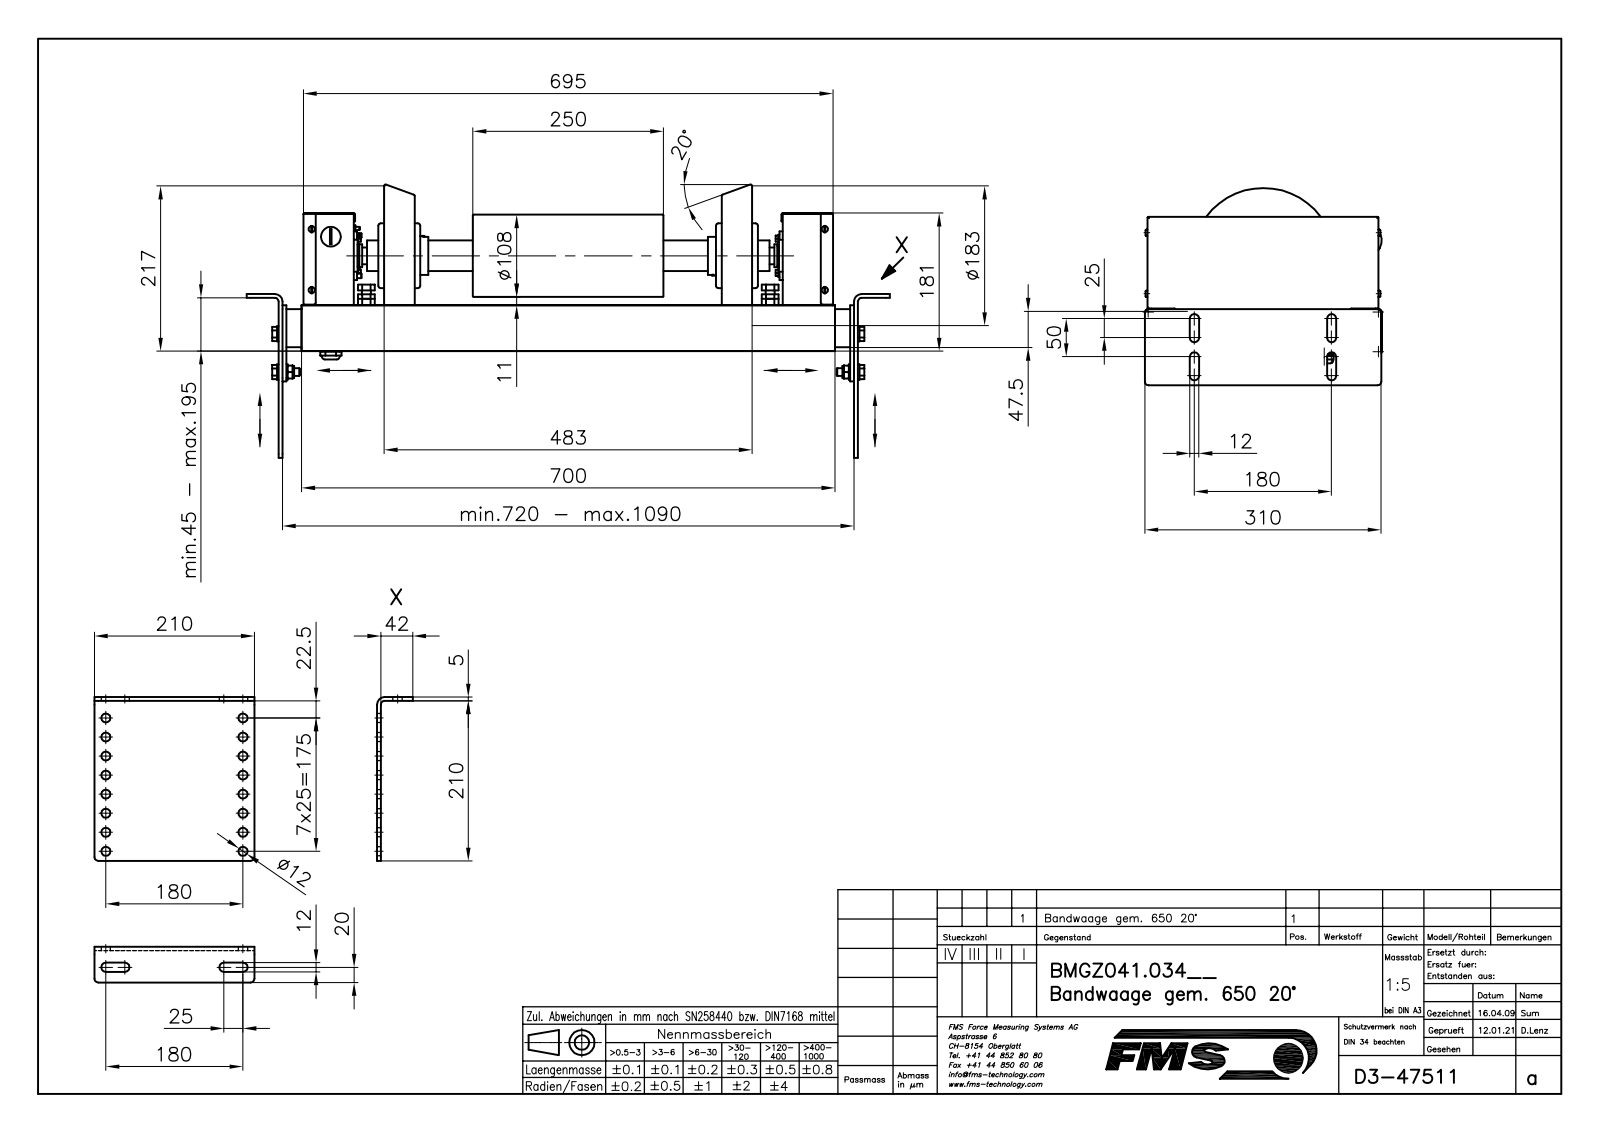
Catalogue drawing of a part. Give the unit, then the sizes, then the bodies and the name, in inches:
Units: inches
Overall size (bounding box): 33.228 × 14.122 × 12.232
Round holes (diameter × count): ⌀0.472 ×17, ⌀0.197 ×6, ⌀0.138 ×4, ⌀0.193 ×4, ⌀0.252 ×4, ⌀0.342 ×4, ⌀0.344 ×4, ⌀0.394 ×4, ⌀0.413 ×4, ⌀0.42 ×4, ⌀0.583 ×4, ⌀0.161 ×3
Round bosses / shafts (diameter × count): ⌀0.472 ×11, ⌀0.323 ×8, ⌀0.165 ×8, ⌀0.787 ×6, ⌀0.394 ×6, ⌀0.197 ×5, ⌀0.63 ×4, ⌀0.437 ×4
Partial cylindrical surfaces — rounded edges, fillets, slot ends (radius × count): R0.079 ×34, R0.039 ×24, R0.157 ×16, R0.197 ×16, R0.236 ×14, R0.138 ×8, R0.089 ×6, R0.02 ×4
Main face-to-face distances: 0.157, 0.197, 0.039, 10.63, 1.417, 10.472, 1.26, 2.205, 10.787, 1.575
Hole centre spacings: 0.984, 7.155, 1.969, 7.355, 2.953, 7.677, 3.937, 7.087
Volume: 380.3 in³ · Surface area: 4 915 in²
Bodies: 161 solids, 2732 faces (1379 planar, 974 cylindrical, 379 other)
Part name (STEP PRODUCT): B47511_STP; B50029; B46957; B4695602 (+8 more)
STEP written by: Mechanical Desktop 2009 (CONFIG_CONTROL_DESIGN)
